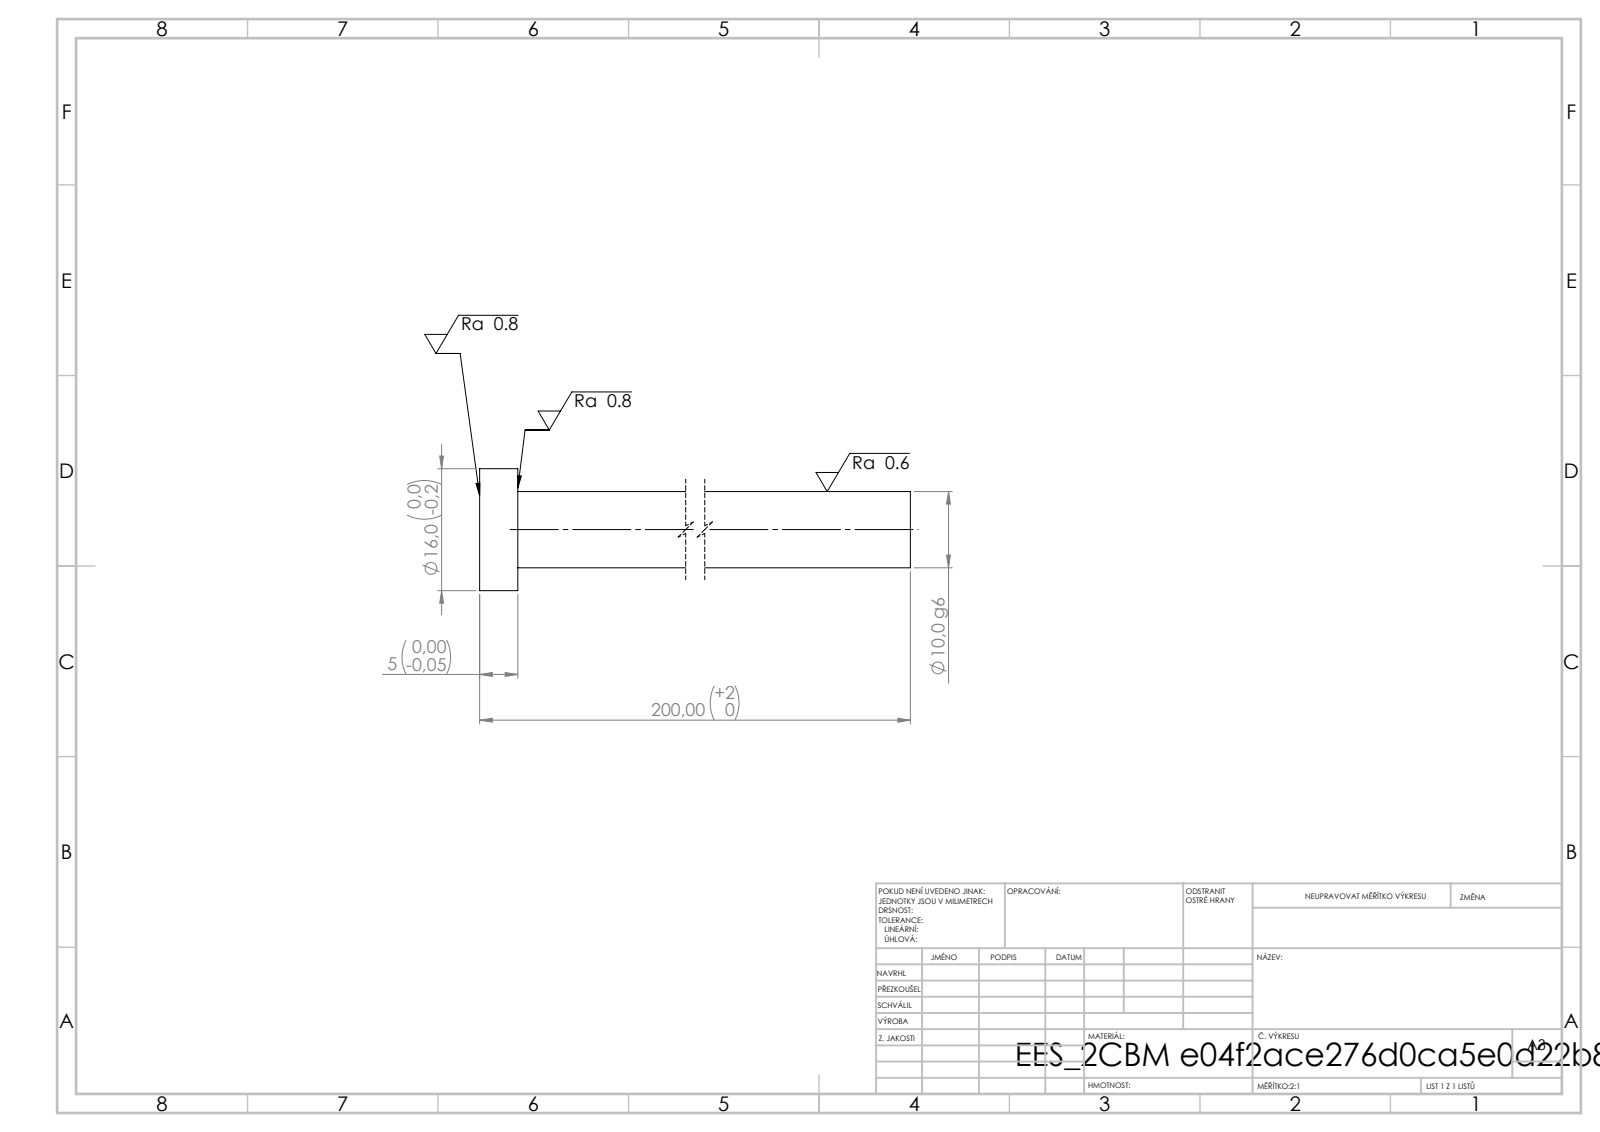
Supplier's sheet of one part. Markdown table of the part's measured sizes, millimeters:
| quantity | value |
| --- | --- |
| STEP written by | SolidWorks 2019 (CONFIG_CONTROL_DESIGN) |
| units | millimeters |
| bodies | 1 solid, 7 faces (3 planar, 4 cylindrical, 0 other) |
| overall size | 200 × 16 × 16 |
| volume | 16 321 mm³ |
| surface area | 6 780 mm² |
| round bosses / shafts (diameter × count) | 16 × 1, 10 × 1 |
| main face-to-face distances | 5, 200, 195 |
